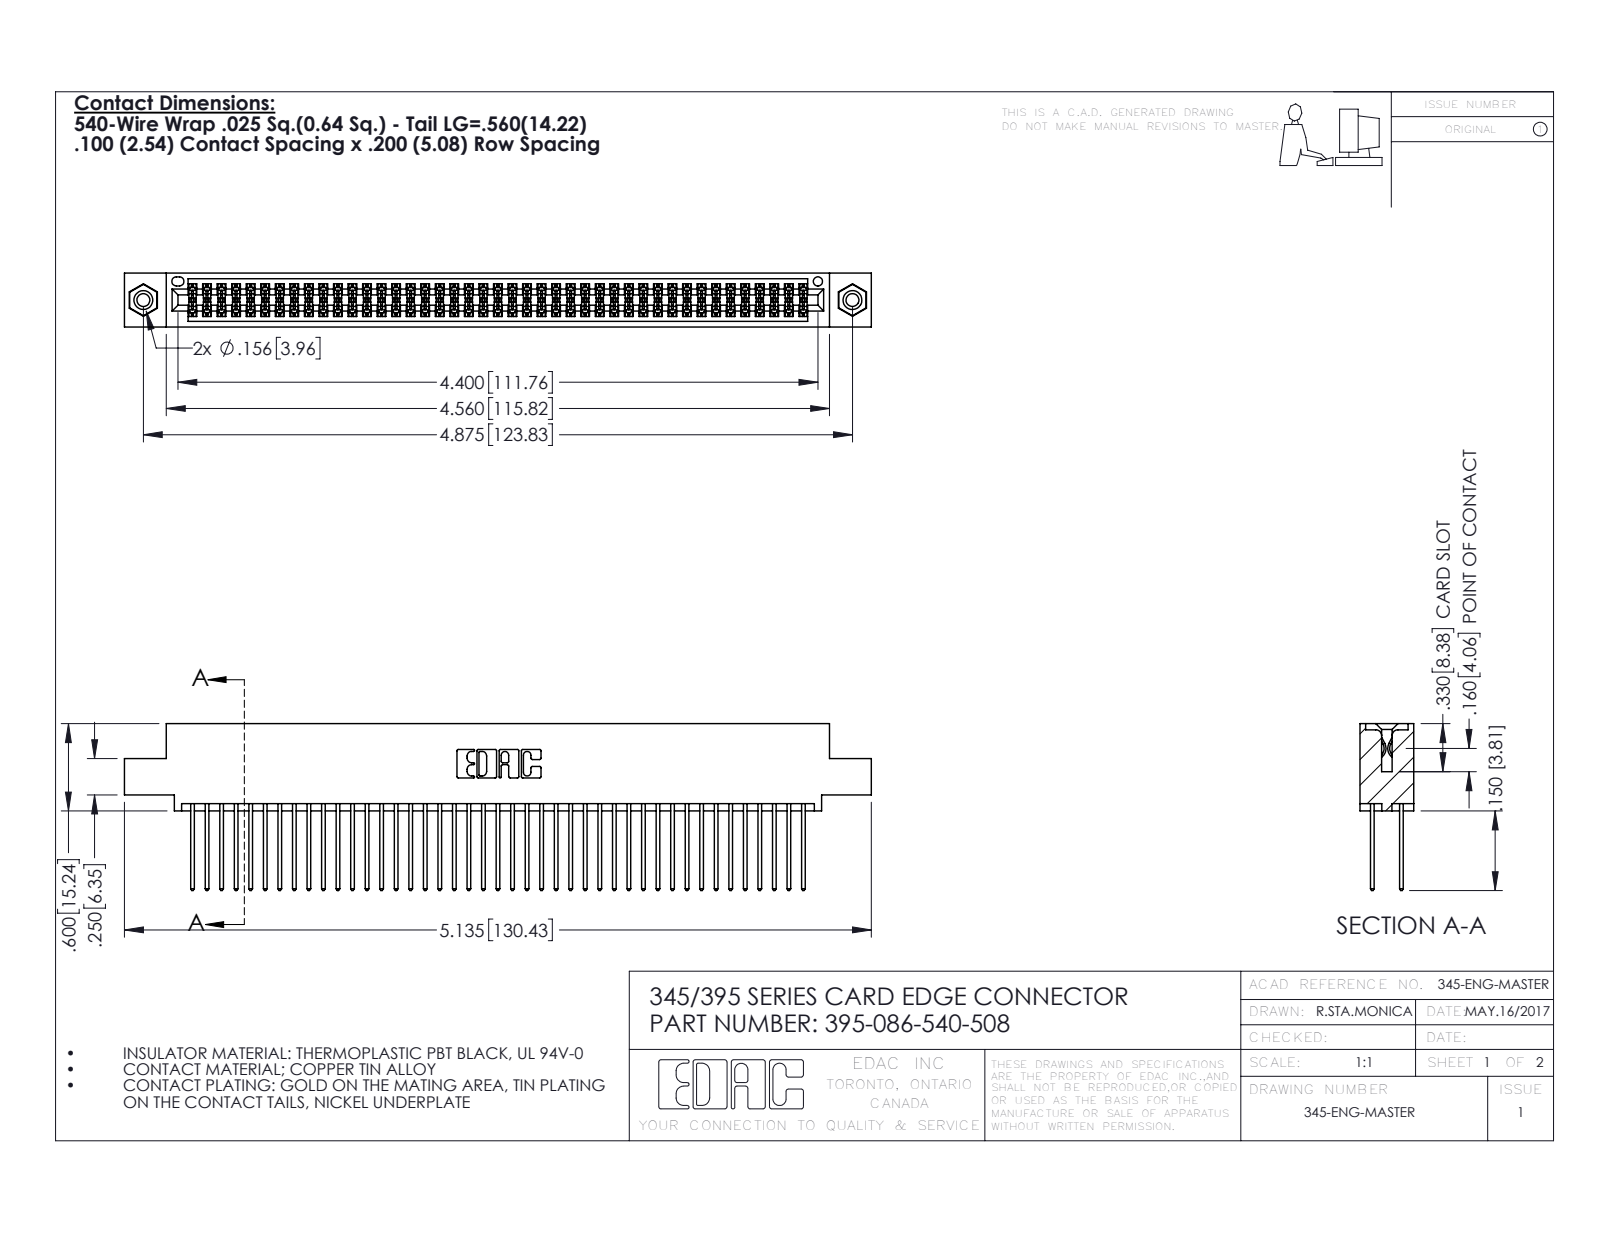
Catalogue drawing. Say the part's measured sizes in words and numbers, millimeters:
The part is named "345-292-001_345-293-140; 345-250-001_345-250-003-102; 345 Part_0.110 Offset - 0.156 Dia-TI; 395-086-540-508". Its 3-D file was written by "SolidWorks 2016 (CONFIG_CONTROL_DESIGN)". It is 89 solids with 4490 faces: 2954 planar, 1520 cylindrical and 16 other. Overall it measures 130.4 by 29.1 by 9.4 millimeters. Its volume is 12 900 cubic millimeters and its surface area 20 740 square millimeters. Round holes: 2 of diameter 2.3, 2 of diameter 3.2, 2 of diameter 4, 1 of diameter 1.6. Round bosses or shafts: 2 of diameter 3.9. Partial cylindrical surfaces (rounded edges, fillets, slot ends): 129 of radius 0.2, 86 of radius 0.3, 22 of radius 0.3, 6 of radius 0.2, 6 of radius 0.8, 3 of radius 0.7, 2 of radius 0.4, 2 of radius 0.5. The main face-to-face distances are 1.8, 7.6, 5.1, 2.5, 6.9, 0.6, 9.4, 5.7, 4.4, 3.8. The hole center spacings are 6.9, 117.8, 123.8.
